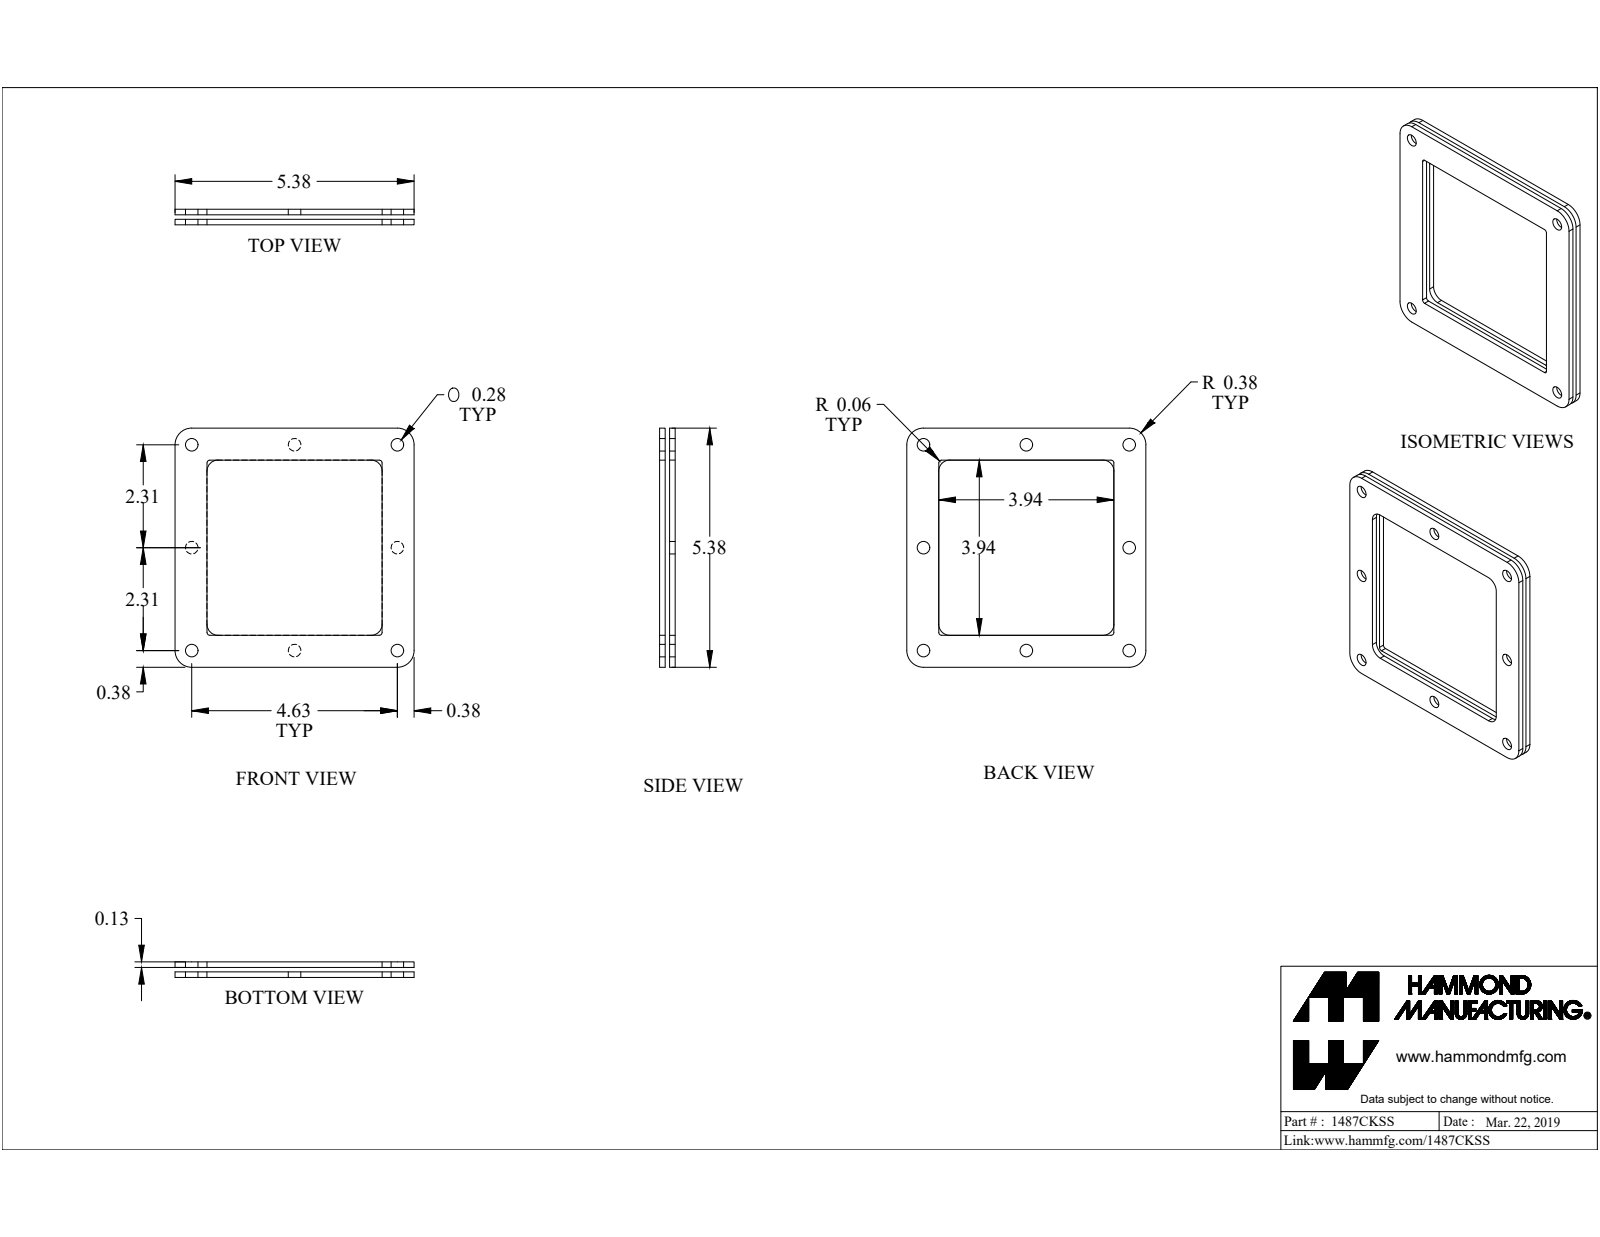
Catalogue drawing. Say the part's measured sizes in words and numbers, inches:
The part is named "1487CKSS". Its 3-D file was written by "SolidWorks 2019 (CONFIG_CONTROL_DESIGN)". It is 7 solids with 213 faces: 126 planar, 71 cylindrical and 16 other. Overall it measures 5.375 by 5.375 by 1.916 inches. Its volume is 3.399 cubic inches and its surface area 66.22 square inches. Round holes: 8 of diameter 0.281, 2 of diameter 0.258, 2 of diameter 0.35, 1 of diameter 0.196. Round bosses or shafts: 2 of diameter 0.5, 2 of diameter 0.25. Partial cylindrical surfaces (rounded edges, fillets, slot ends): 12 of radius 0.02, 5 of radius 0.25, 4 of radius 0.062, 4 of radius 0.375. The main face-to-face distances are 0.125, 0.125, 0.225, 0.1, 0.35, 0.225, 5.375, 0.719, 4.656, 0.718. The hole center spacings are 2.313, 3.27, 5.171, 4.625, 6.541.
